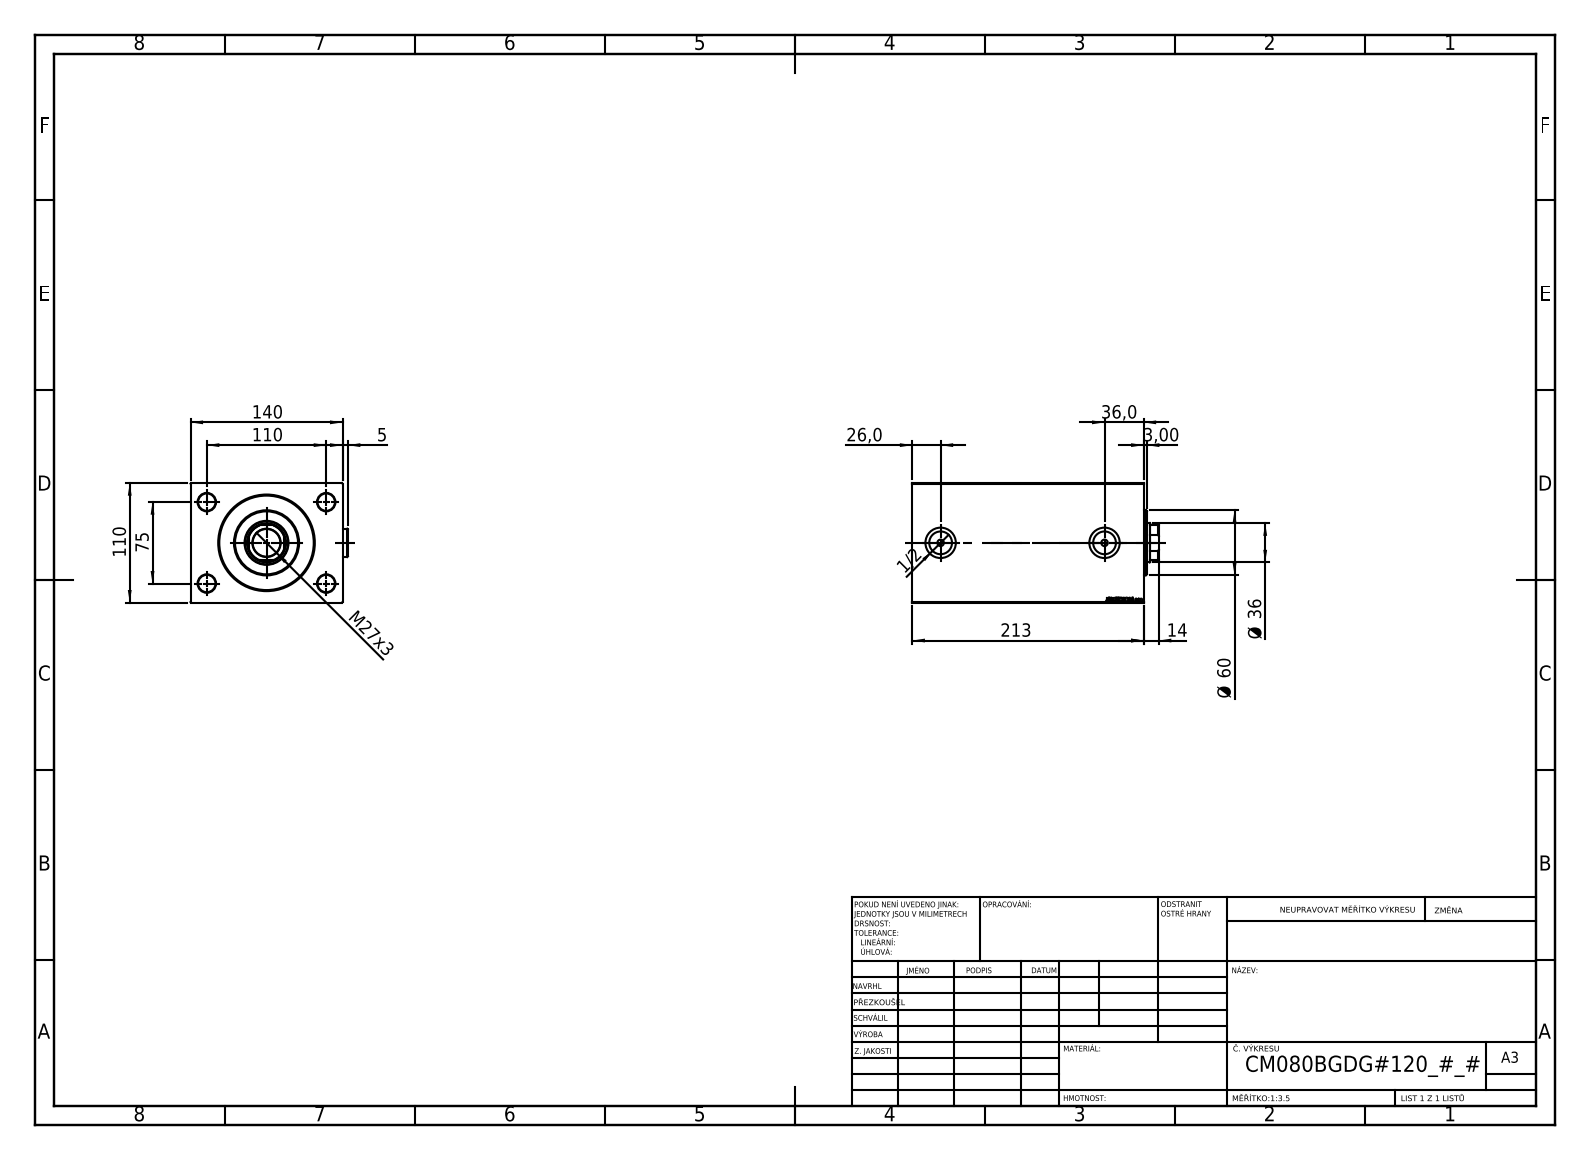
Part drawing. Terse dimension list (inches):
name: V450CM_B_Body; V450CM_B_VCP; Zatka_OIL_PORT; V450CM_VC_B
written by: SolidWorks 2019 (CONFIG_CONTROL_DESIGN)
unit: in
bodies: 5 solids, 938 faces (436 planar, 72 cylindrical, 430 other)
size: 8.937 × 5.705 × 4.331
volume: 166.8 in³; area: 410.9 in²
holes: 4× ⌀0.63, 2× ⌀0.236, 2× ⌀0.825, 2× ⌀1.102, 1× ⌀1.004, 1× ⌀1.417, 1× ⌀1.555, 1× ⌀1.594, 1× ⌀3.15, 1× ⌀3.228, 1× ⌀3.425
bosses: 2× ⌀1.024, 1× ⌀2.362
rounds: 1× R0.689
face distances: 4.331, 5.512, 8.386, 7.559, 0.827, 0.551, 7.008, 7.835, 5.276, 4.724
hole spacings: 2.621, 2.953, 4.331, 5.242, 5.945
